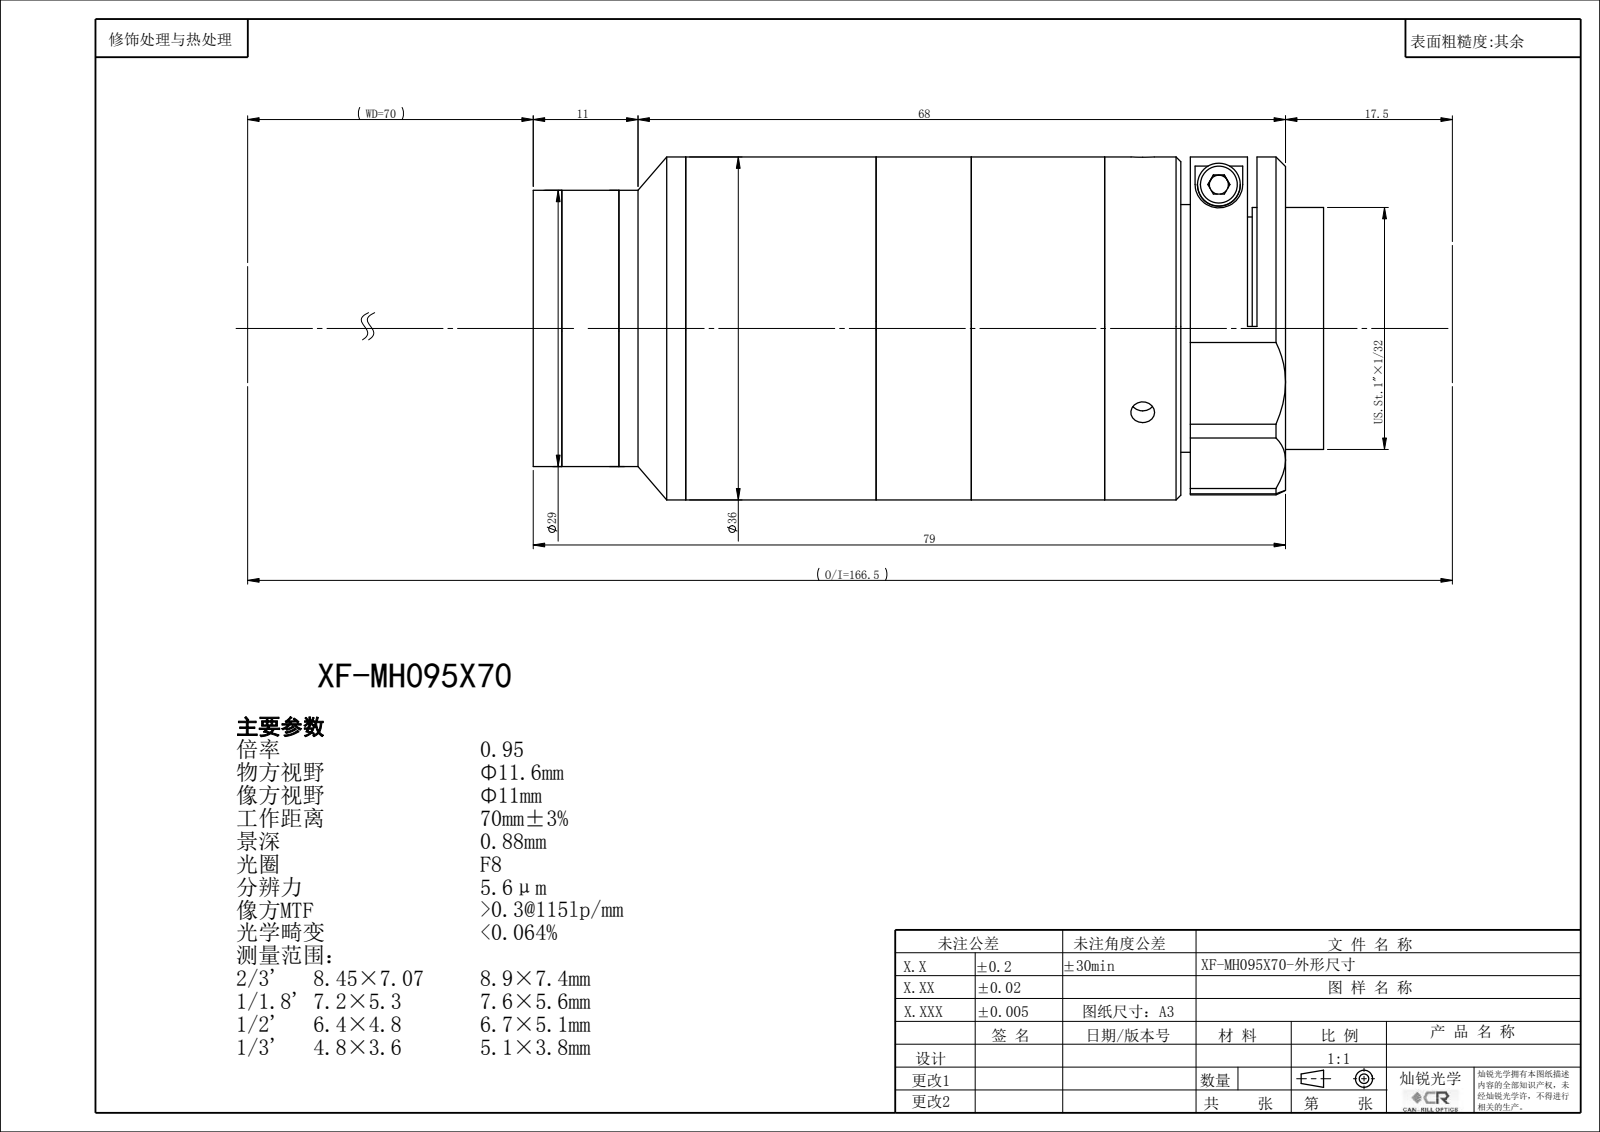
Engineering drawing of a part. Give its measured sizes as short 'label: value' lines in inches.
name: XF-MH095X70
written by: SolidWorks 2022 (CONFIG_CONTROL_DESIGN)
unit: in
bodies: 0 solids, 132 faces (66 planar, 44 cylindrical, 22 other)
size: 3.268 × 1.418 × 1.417
holes: 3× ⌀0.098, 1× ⌀0.551, 1× ⌀0.882, 1× ⌀0.945, 1× ⌀0.98, 1× ⌀1.039, 1× ⌀1.063
bosses: 1× ⌀1.417, 1× ⌀1.339, 1× ⌀1.142, 1× ⌀1
face distances: 1.181, 0.787, 0.747, 2.213, 2.96, 0.059, 2.901, 0.688, 1.662, 0.551
